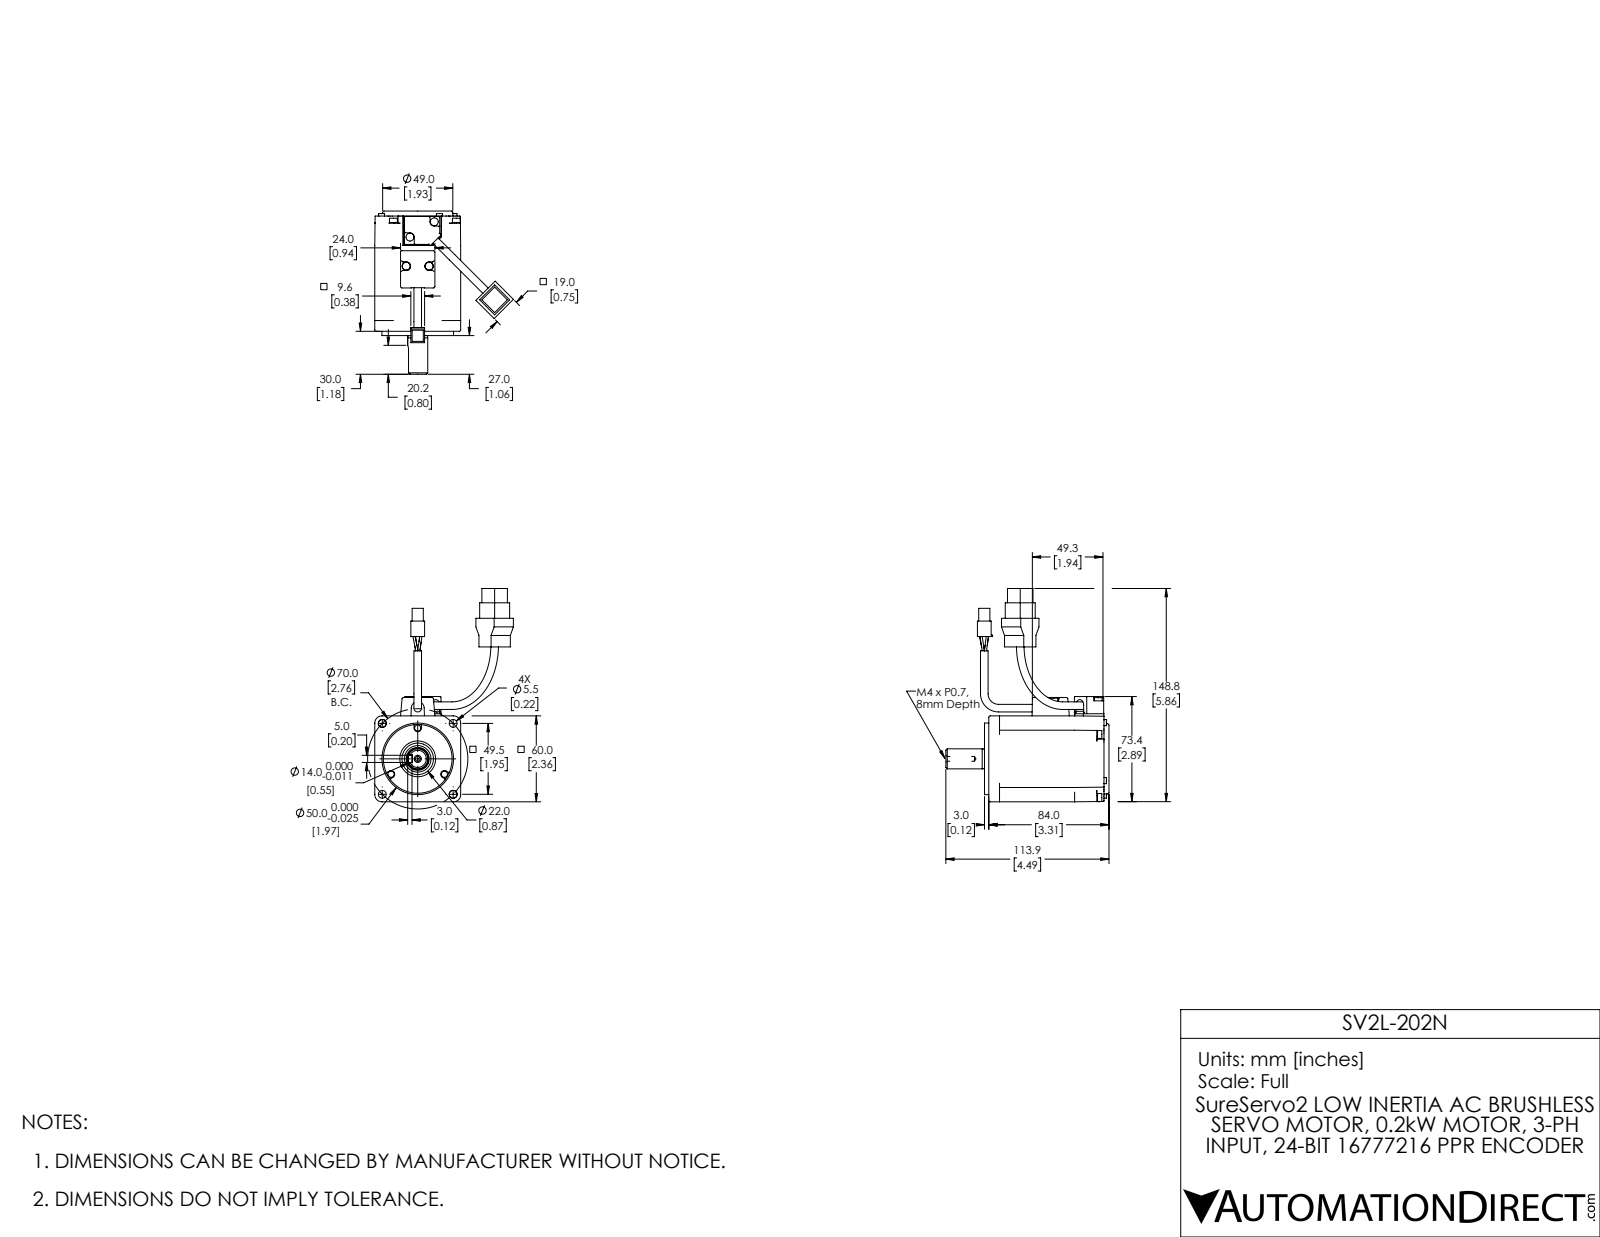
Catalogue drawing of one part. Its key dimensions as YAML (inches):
part_name: "ECM-A3H-CX0602RSX P1 Coord fXT"
step_written_by: "SolidWorks 2017 (AUTOMOTIVE_DESIGN)"
units: inches
bodies: {solids: 1, faces: 612, planar: 191, cylindrical: 226, other: 195}
overall_size: [5.863, 4.486, 3.811]
volume: 18.32
surface_area: 60.21
round_holes:
  - {diameter: 0.13, count: 3}
  - {diameter: 0.217, count: 2}
  - {diameter: 0.236, count: 1}
  - {diameter: 0.63, count: 1}
  - {diameter: 0.866, count: 1}
  - {diameter: 0.984, count: 1}
  - {diameter: 1.89, count: 1}
round_bosses_or_shafts:
  - {diameter: 0.217, count: 8}
  - {diameter: 0.169, count: 7}
  - {diameter: 0.228, count: 6}
  - {diameter: 0.209, count: 4}
  - {diameter: 0.059, count: 4}
  - {diameter: 1.969, count: 1}
  - {diameter: 1.929, count: 1}
  - {diameter: 0.728, count: 1}
partial_cylinders:
  - {radius: 0.02, count: 24}
  - {radius: 0.039, count: 20}
  - {radius: 0.079, count: 16}
  - {radius: 0.006, count: 12}
  - {radius: 0.012, count: 12}
  - {radius: 0.118, count: 10}
  - {radius: 0.087, count: 6}
  - {radius: 0.197, count: 4}
face_to_face_distances: [2.362, 0.394, 0.098, 3.305, 3.404, 0.138, 3.266, 3.167, 1.969, 0.043]
hole_center_spacings: [1.378, 0.791, 2.713, 2.756, 2.898]
